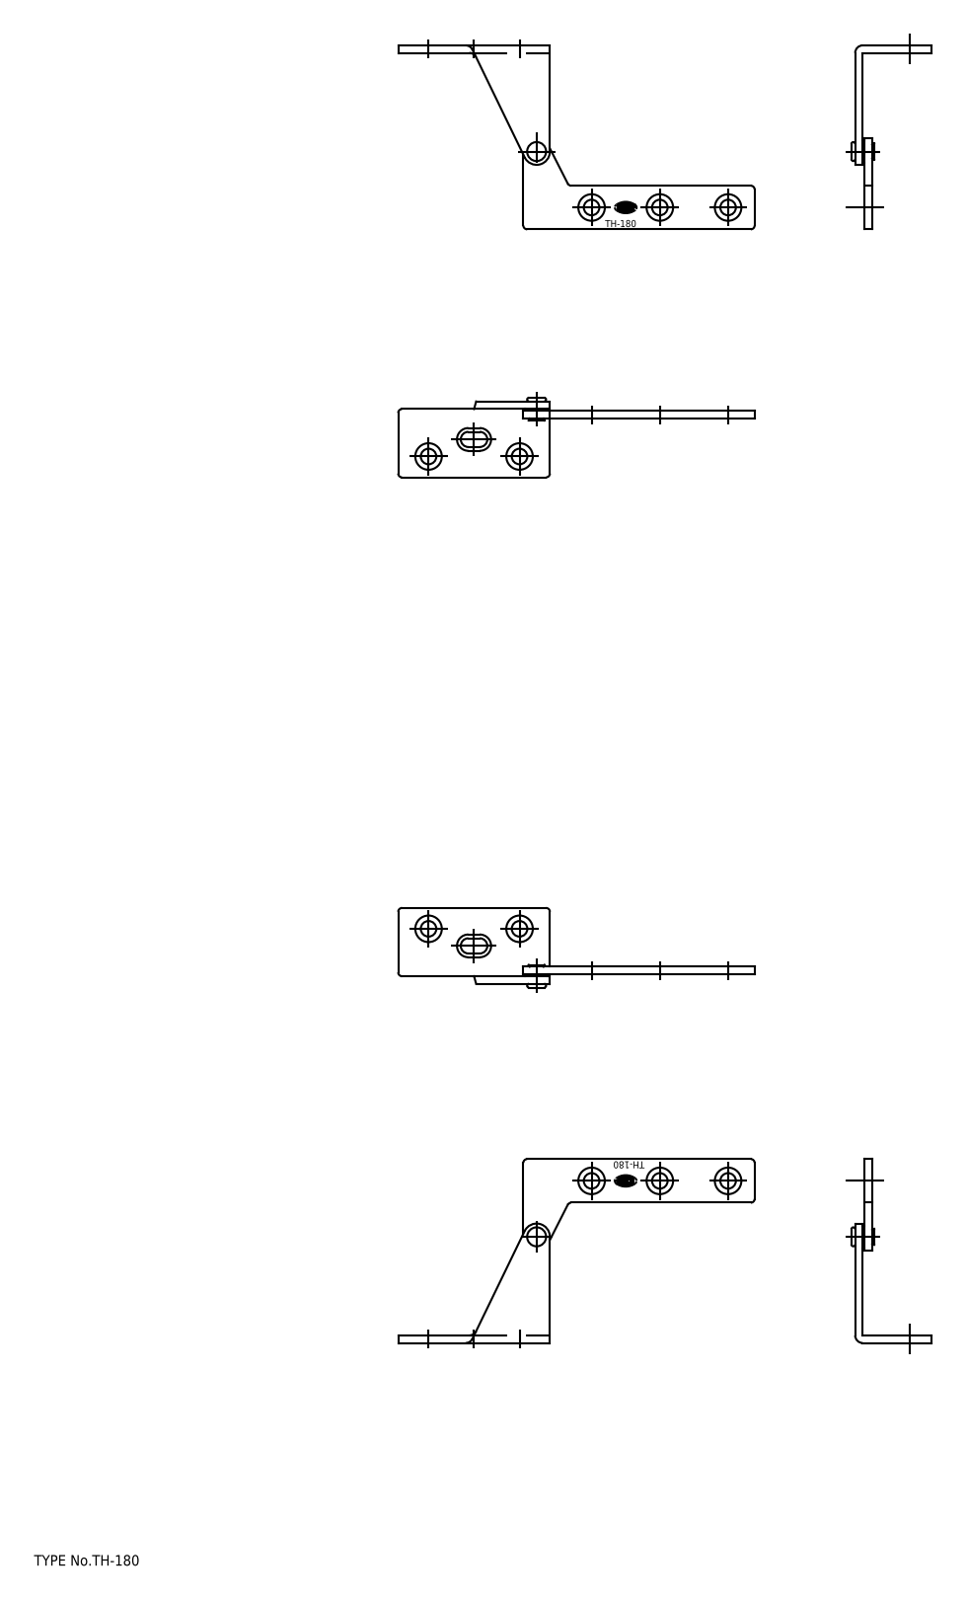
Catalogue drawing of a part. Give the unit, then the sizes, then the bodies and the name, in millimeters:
Units: millimetres
Overall size (bounding box): 67 × 61 × 31.5
Round holes (diameter × count): ⌀4.1 ×7, ⌀3.2 ×1
Round bosses / shafts (diameter × count): ⌀6 ×1, ⌀3 ×1
Partial cylindrical surfaces — rounded edges, fillets, slot ends (radius × count): R1 ×10, R2 ×6, R3.5 ×1
Main face-to-face distances: 2, 2.5, 60.5, 58, 0.5, 58.5, 56, 4.5, 62.5, 63
Hole centre spacings: 36, 18, 24, 43.27, 20.68, 35.69, 52.61
Volume: 7 249 mm³ · Surface area: 9 226 mm²
Bodies: 8 solids, 144 faces (52 planar, 64 cylindrical, 28 other)
Part name (STEP PRODUCT): シャフト（右下・左上用）; ヒンジピース(A); ヒンジピース(B); ワッシャー（右下・左上用） (+4 more)
STEP written by: spGate 16.7.1 (AUTOMOTIVE_DESIGN)
